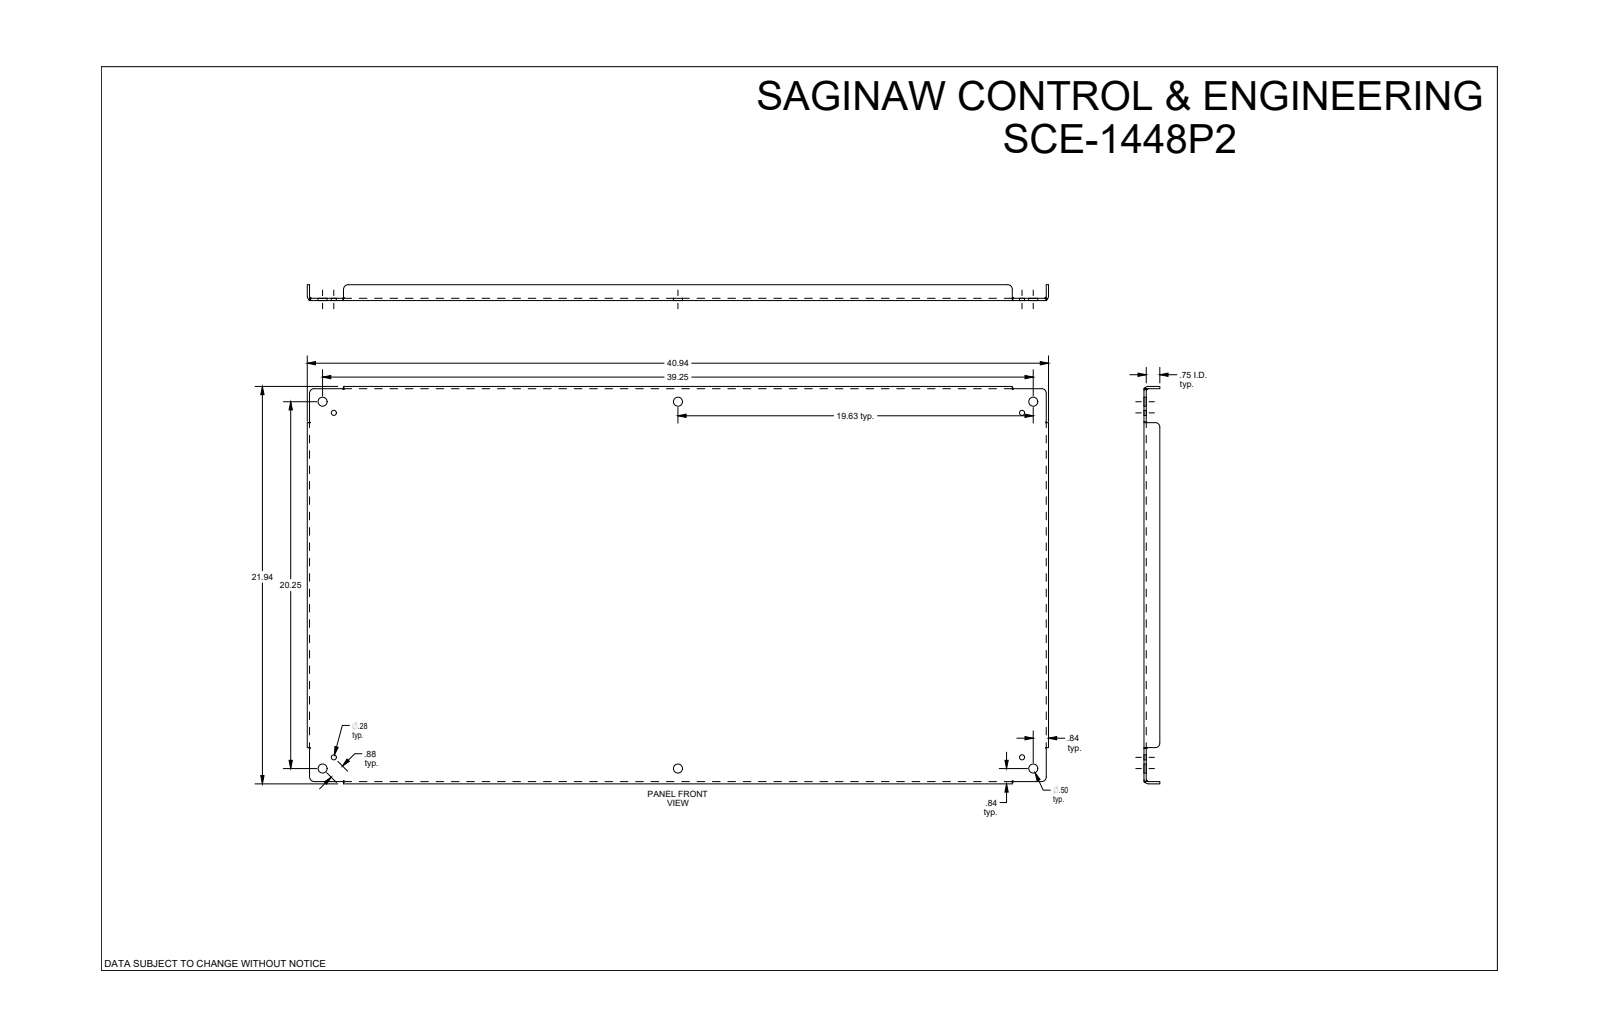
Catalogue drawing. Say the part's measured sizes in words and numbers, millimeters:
The part is named "SCE-1448P2". Its 3-D file was written by "SolidWorks 2019 (CONFIG_CONTROL_DESIGN)". It is 1 solid with 84 faces: 30 planar, 30 cylindrical and 24 other. Overall it measures 1039.8 by 557.2 by 22.2 millimeters. Its volume is 1 984 000 cubic millimeters and its surface area 1 261 000 square millimeters. Round holes: 6 of diameter 12.7, 4 of diameter 7.1. Partial cylindrical surfaces (rounded edges, fillets, slot ends): 8 of radius 6.4, 4 of radius 2.8, 4 of radius 6. The main face-to-face distances are 3.2, 3.2, 554.1, 550.8, 557.2, 1036.7, 19.1, 22.2, 1033.4, 1039.8. The hole center spacings are 22.2, 483, 498.5, 498.9, 694.1, 716.3, 981.4, 1100.7.
